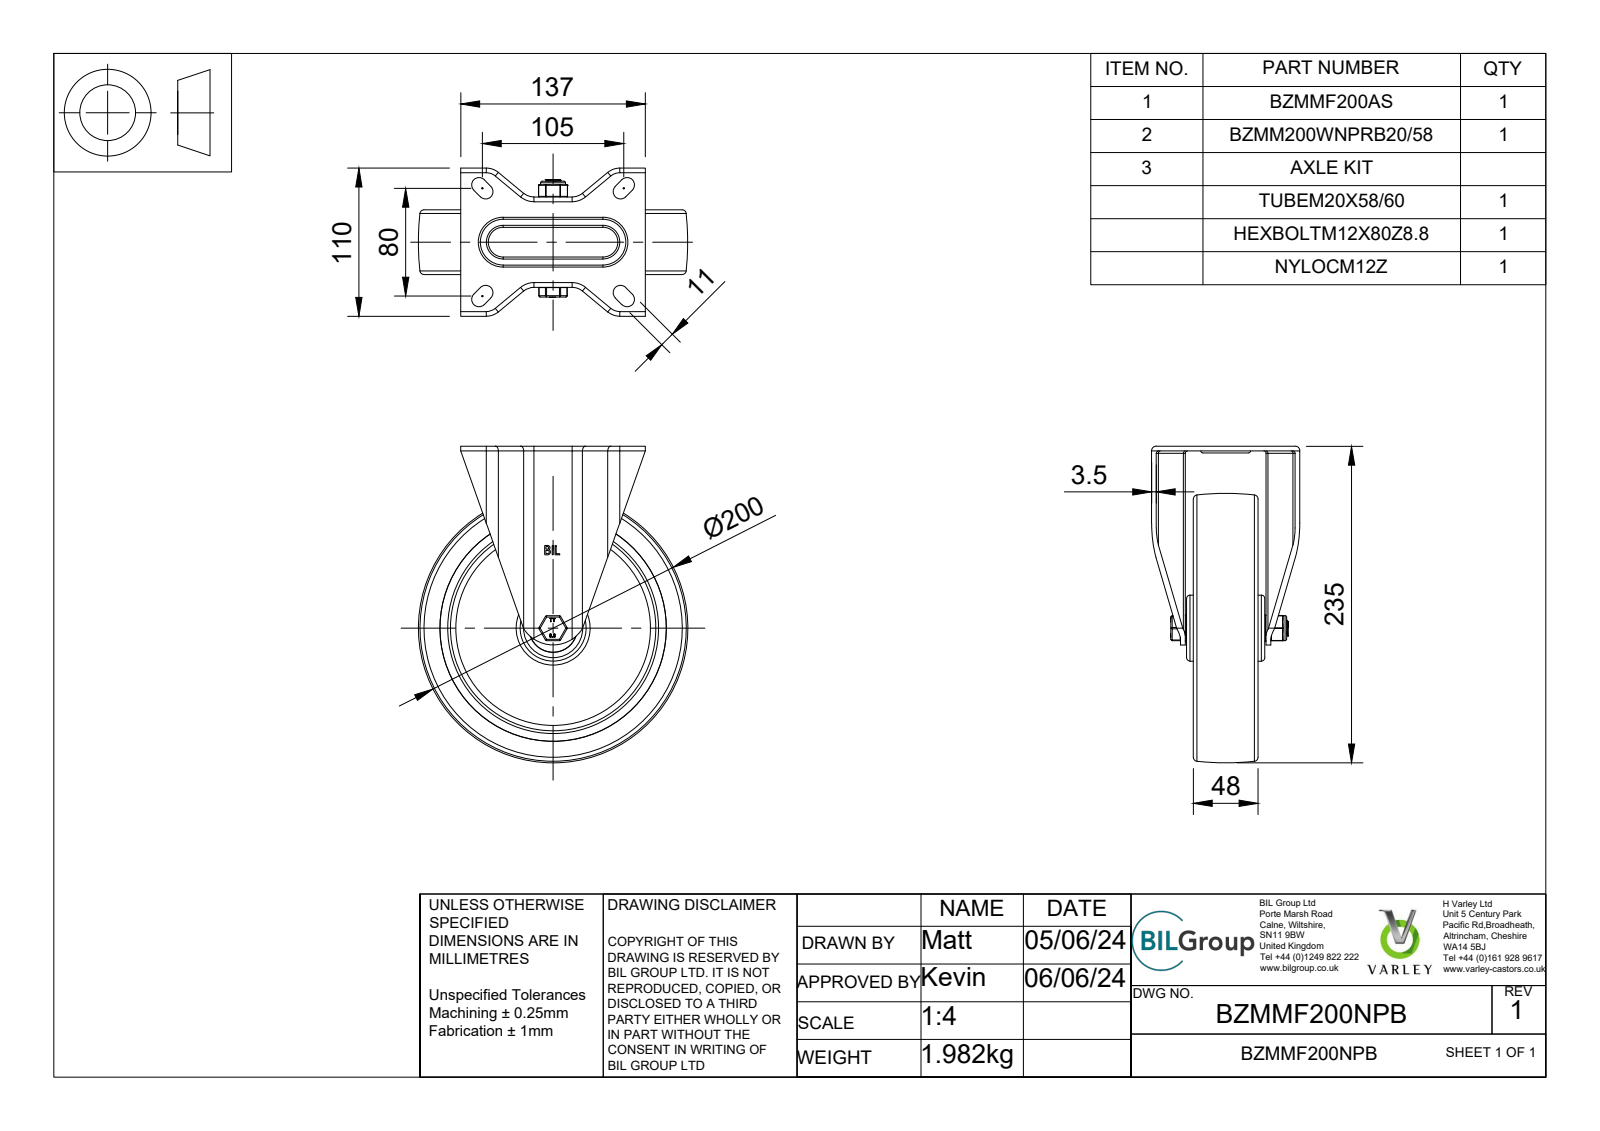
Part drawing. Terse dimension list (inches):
name: BZMMF200NPB v3; BZMMF200AS v1; BZMMF200AS; ZINC PLATED, PRESSED STEEL BRACKET (+8 more)
written by: Autodesk Translation Framework v13.14.0.145 (AUTOMOTIVE_DESIGN)
unit: in
bodies: 19 solids, 502 faces (216 planar, 178 cylindrical, 108 other)
size: 9.252 × 7.874 × 4.331
volume: 58.8 in³; area: 439.4 in²
holes: 1× ⌀0.472, 1× ⌀0.48, 1× ⌀0.551, 1× ⌀0.787, 1× ⌀0.807, 1× ⌀1.181, 1× ⌀1.417, 1× ⌀6.004, 1× ⌀6.614
bosses: 10× ⌀0.197, 1× ⌀1.929, 1× ⌀1.409, 1× ⌀1.161, 1× ⌀0.778, 1× ⌀0.728, 1× ⌀0.709, 1× ⌀0.466
rounds: 18× R0.02, 12× R0.039, 8× R0.059, 8× R0.069, 8× R0.138, 8× R0.217, 4× R0.236, 4× R0.276
face distances: 1.063, 0.138, 0.236, 0.827, 2.126, 0.969, 1.299, 1.89, 1.201, 0.374
